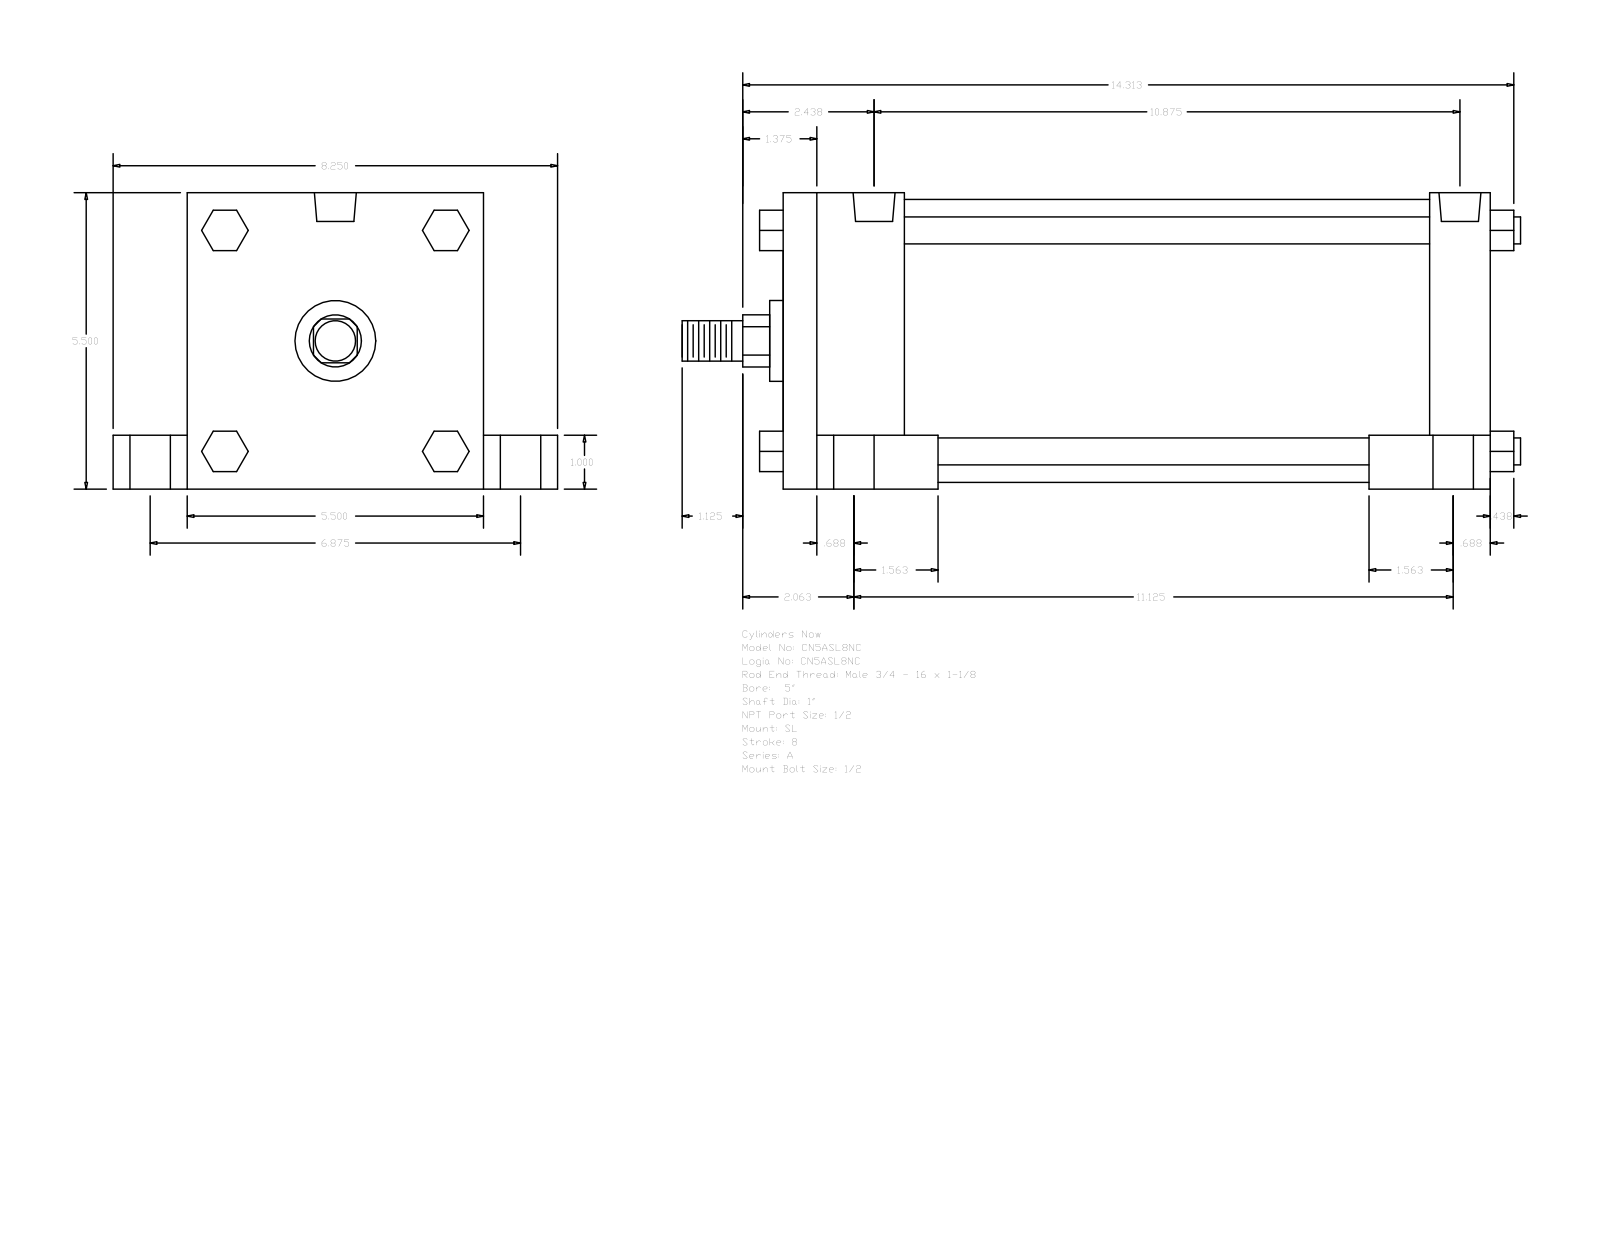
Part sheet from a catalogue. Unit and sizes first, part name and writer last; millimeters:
Units: millimetres
Overall size (bounding box): 395.29 × 209.55 × 139.7
Round holes (diameter × count): ⌀8.73 ×4, ⌀19.05 ×4, ⌀25.4 ×4, ⌀19.77 ×2
Round bosses / shafts (diameter × count): ⌀12.7 ×4, ⌀133.35 ×1, ⌀38.1 ×1, ⌀25.4 ×1, ⌀19.05 ×1
Partial cylindrical surfaces — rounded edges, fillets, slot ends (radius × count): R12.29 ×1
Main face-to-face distances: 139.7, 333.38, 28.58, 25.4, 114.3, 34.93, 174.63, 57.15, 304.8, 247.65
Hole centre spacings: 2.39, 87.31, 87.37, 87.83, 88.12, 174.62, 271.45, 273.84
Bodies: 0 solids, 150 faces (114 planar, 36 cylindrical, 0 other)
Part name (STEP PRODUCT): A_SL__0500_1
STEP written by: GSSL Pune (CONFIG_CONTROL_DESIGN)
